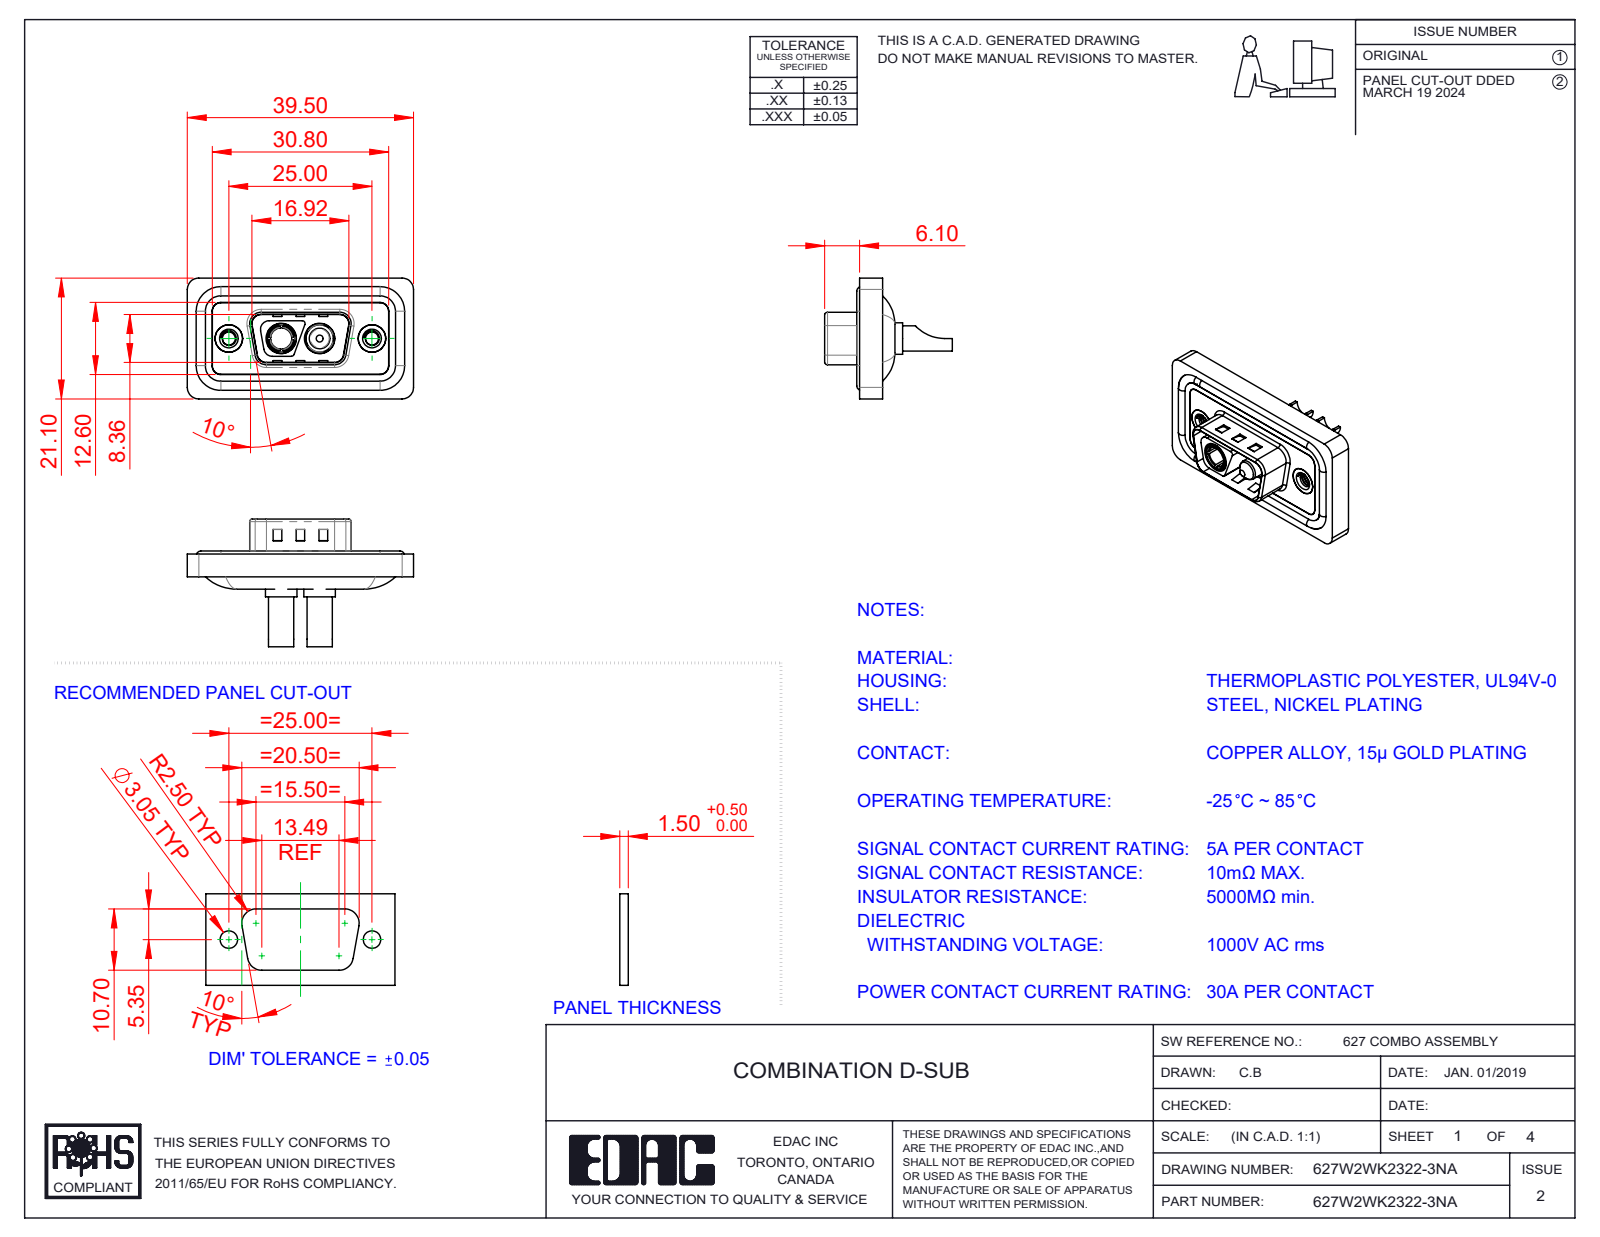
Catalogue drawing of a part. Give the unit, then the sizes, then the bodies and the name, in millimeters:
Units: millimetres
Overall size (bounding box): 39.5 × 22.3 × 21.1
Round holes (diameter × count): ⌀2.26 ×2, ⌀3.5 ×2, ⌀4 ×2, ⌀4.8 ×2, ⌀4.85 ×2, ⌀5 ×2, ⌀5.3 ×2, ⌀3.7 ×1
Round bosses / shafts (diameter × count): ⌀1.6 ×4, ⌀5.5 ×2, ⌀5.2 ×2, ⌀4.9 ×2, ⌀4.75 ×2, ⌀4.4 ×2, ⌀3.75 ×2, ⌀4.96 ×1
Partial cylindrical surfaces — rounded edges, fillets, slot ends (radius × count): R1.5 ×24, R2 ×18, R0.5 ×10, R1.6 ×8, R0.25 ×4, R0.6 ×4, R0.65 ×4, R0.9 ×4
Main face-to-face distances: 0.4, 1.1, 2.9, 0.5, 3.1, 1.6, 1.5, 2.5, 1.8, 3.2
Hole centre spacings: 9.14, 15.86, 6.72, 25
Volume: 4 604 mm³ · Surface area: 7 555 mm²
Bodies: 11 solids, 544 faces (195 planar, 235 cylindrical, 114 other)
Part name (STEP PRODUCT): 627Combo Housing_2WK2; 627Combo Shell Rear_09 Contacts; 627Combo Waterproof Housing_09 Contacts; 627Combo Threaded Rivet_A (+4 more)
STEP written by: SolidWorks 2023 (CONFIG_CONTROL_DESIGN)
